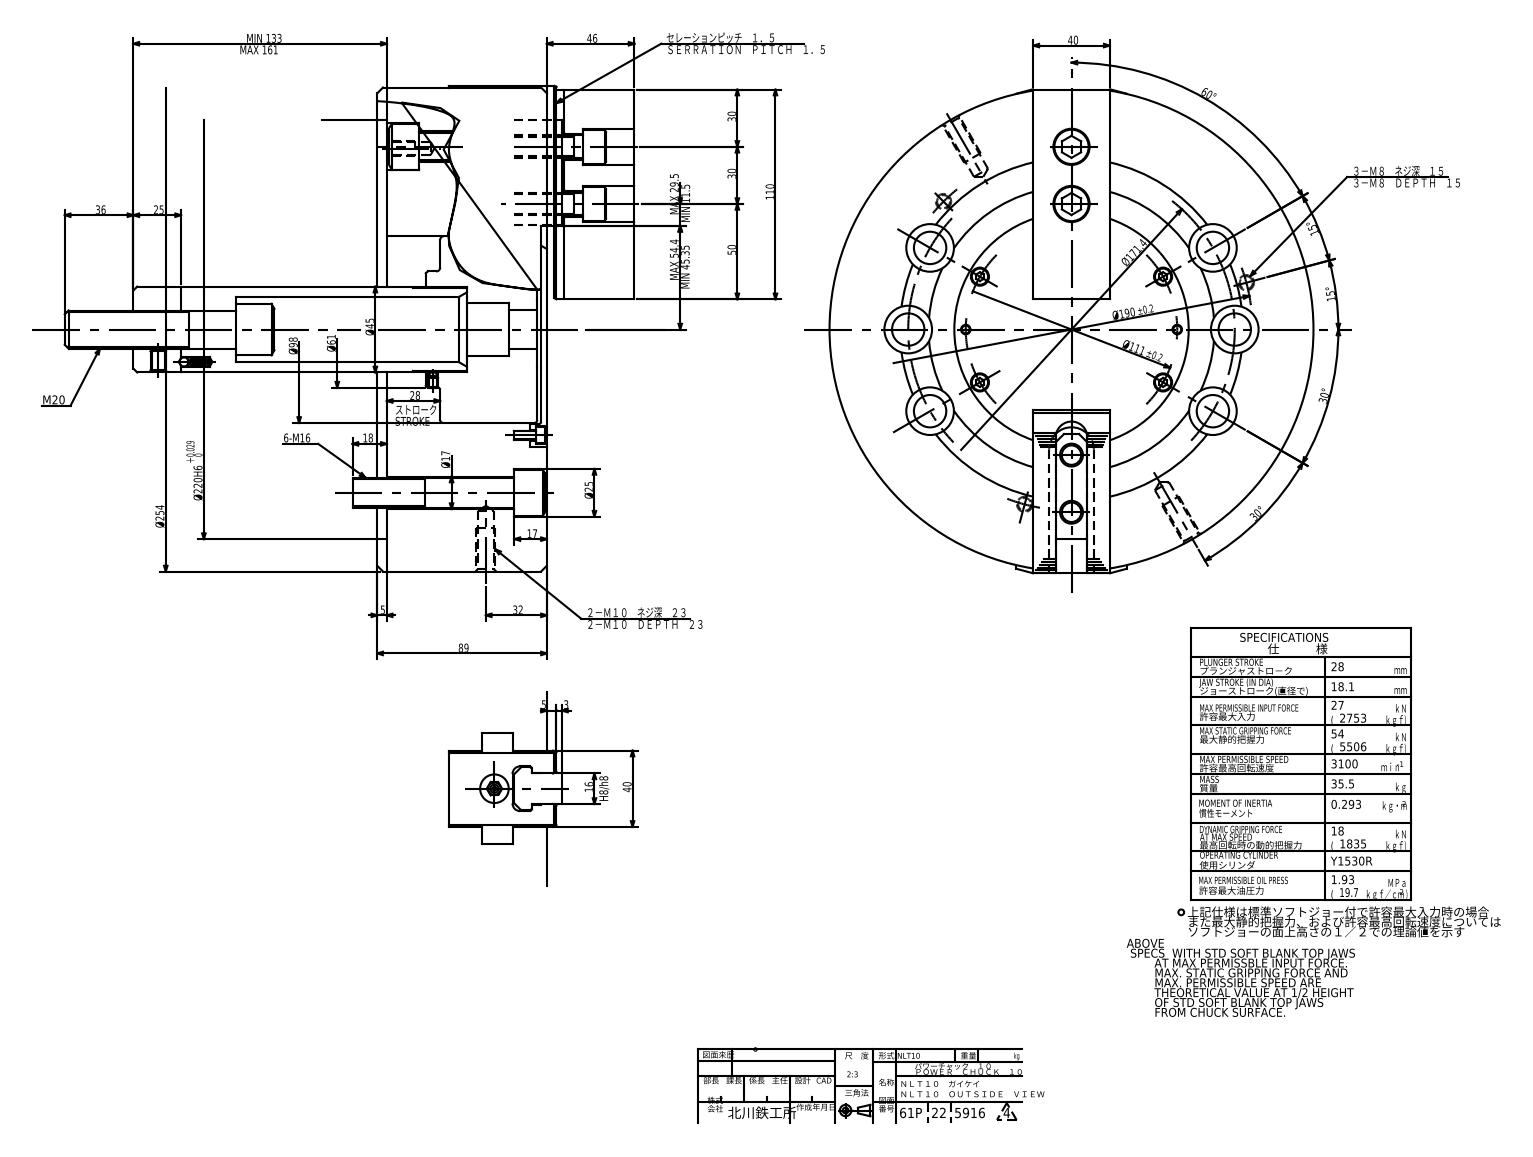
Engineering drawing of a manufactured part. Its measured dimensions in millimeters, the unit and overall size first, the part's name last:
Units: millimetres
Overall size (bounding box): 313.2 × 254 × 254
Round holes (diameter × count): ⌀17 ×8, ⌀25 ×8, ⌀4.2 ×5, ⌀4 ×4, ⌀5.5 ×4, ⌀6.8 ×4, ⌀9.5 ×4, ⌀10.3 ×4, ⌀13 ×4, ⌀19 ×4, ⌀8.5 ×2, ⌀14 ×2
Round bosses / shafts (diameter × count): ⌀24 ×6, ⌀15.68 ×6, ⌀18 ×4, ⌀11.7 ×4, ⌀8.5 ×4, ⌀4.83 ×4, ⌀254 ×1, ⌀98 ×1
Partial cylindrical surfaces — rounded edges, fillets, slot ends (radius × count): R0.8 ×10, R0.4 ×4, R0.6 ×4, R4.5 ×4, R1.2 ×2, R8.3 ×2, R11.75 ×2, R49.5 ×1
Main face-to-face distances: 84, 5, 40, 3, 89, 19, 70, 32.5, 135.2, 130.2
Hole centre spacings: 85.72, 55.5, 17, 24.04, 30.23, 41.65, 44.37, 46.78
Volume: 4 514 000 mm³ · Surface area: 410 614 mm²
Bodies: 1 solid, 2810 faces (1976 planar, 663 cylindrical, 171 other)
STEP written by: ST-DEVELOPER v16.7 (AUTOMOTIVE_DESIGN)
